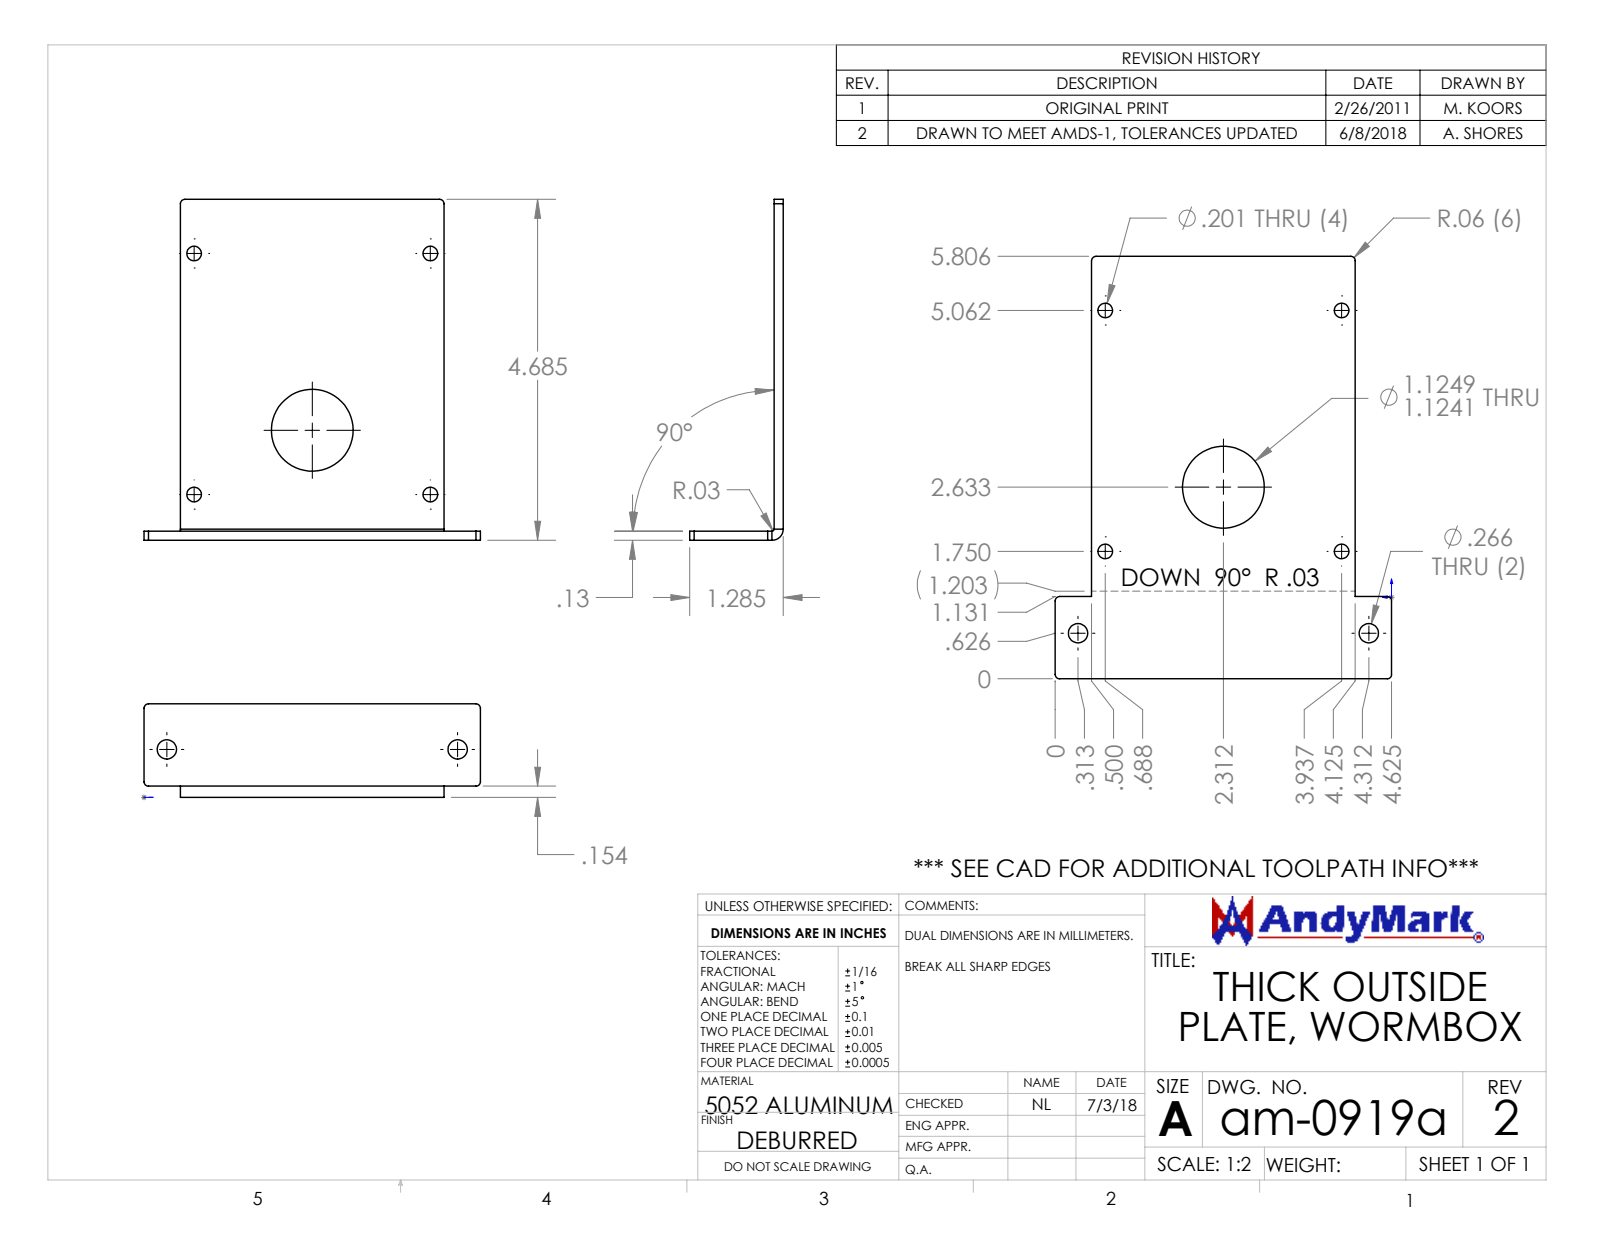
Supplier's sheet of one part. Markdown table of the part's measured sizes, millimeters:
| quantity | value |
| --- | --- |
| part name | am-0919a Output Plate for Wormbox REV2 |
| STEP written by | SolidWorks 2018 (AUTOMOTIVE_DESIGN) |
| units | millimeters |
| bodies | 1 solid, 36 faces (14 planar, 22 cylindrical, 0 other) |
| overall size | 119 × 117.5 × 32.6 |
| volume | 42 900 mm³ |
| surface area | 29 310 mm² |
| round holes (diameter × count) | 5.1 × 4, 6.8 × 2, 28.6 × 1 |
| partial cylindrical surfaces (radius × count) | 1.5 × 6, 0.7 × 1, 3.9 × 1 |
| main face-to-face distances | 3.2, 92.1, 32.6, 29.5, 119, 115.8, 12.7, 104.8, 117.5, 3.9 |
| hole center spacings | 82.5, 84.1, 117.8, 46.9, 47, 74.2, 74.2, 101.6 |
